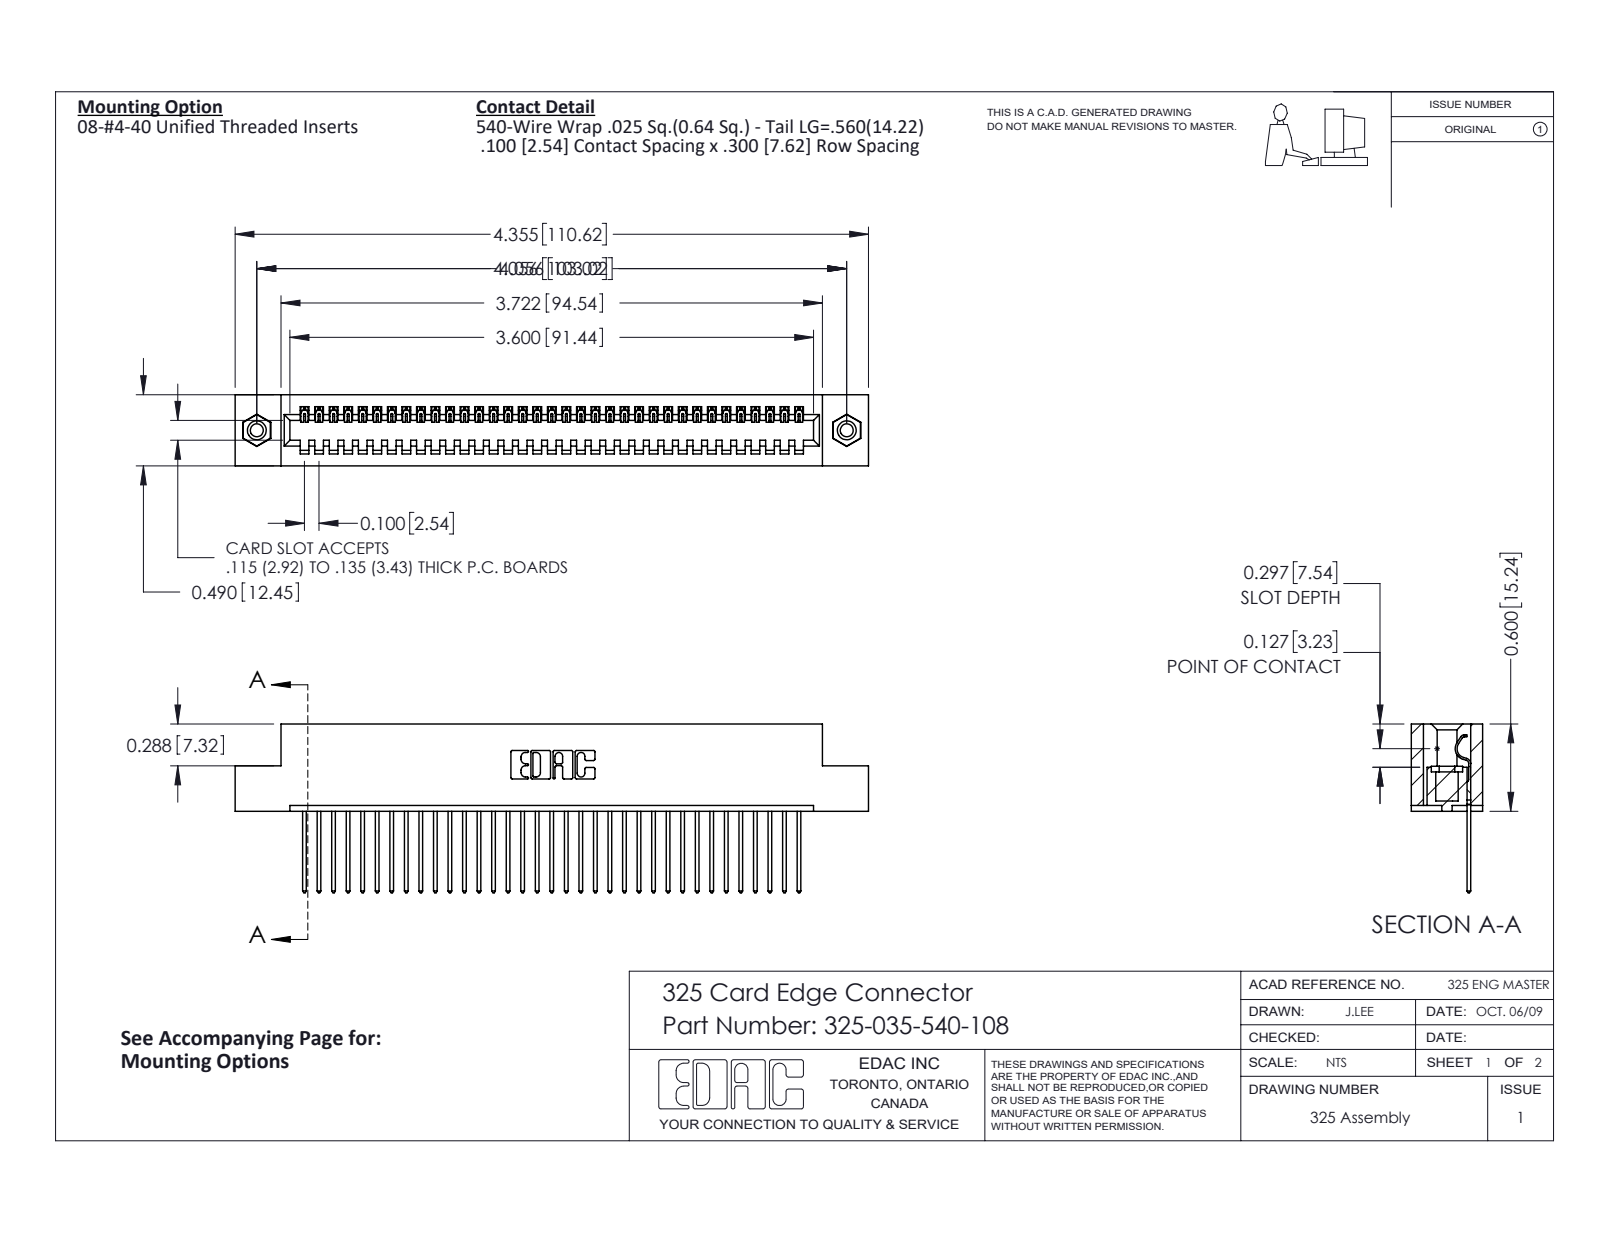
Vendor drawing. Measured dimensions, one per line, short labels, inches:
name: 325-035-540-108; 325 Part_TI; 325-292-001_325-293-140; 345-250-001_345-250-003-102
written by: SolidWorks 2016 (CONFIG_CONTROL_DESIGN)
unit: in
bodies: 38 solids, 2204 faces (1572 planar, 616 cylindrical, 16 other)
size: 4.355 × 1.16 × 0.49
volume: 0.856 in³; area: 24.14 in²
holes: 2× ⌀0.089, 2× ⌀0.125, 2× ⌀0.16
bosses: 2× ⌀0.155
rounds: 70× R0.006, 70× R0.01, 22× R0.01, 6× R0.007, 6× R0.031, 3× R0.026, 1× R0.014, 1× R0.022
face distances: 0.083, 0.407, 0.49, 0.3, 0.107, 0.383, 0.025, 0.325, 0.56, 0.6
hole spacings: 4.056
